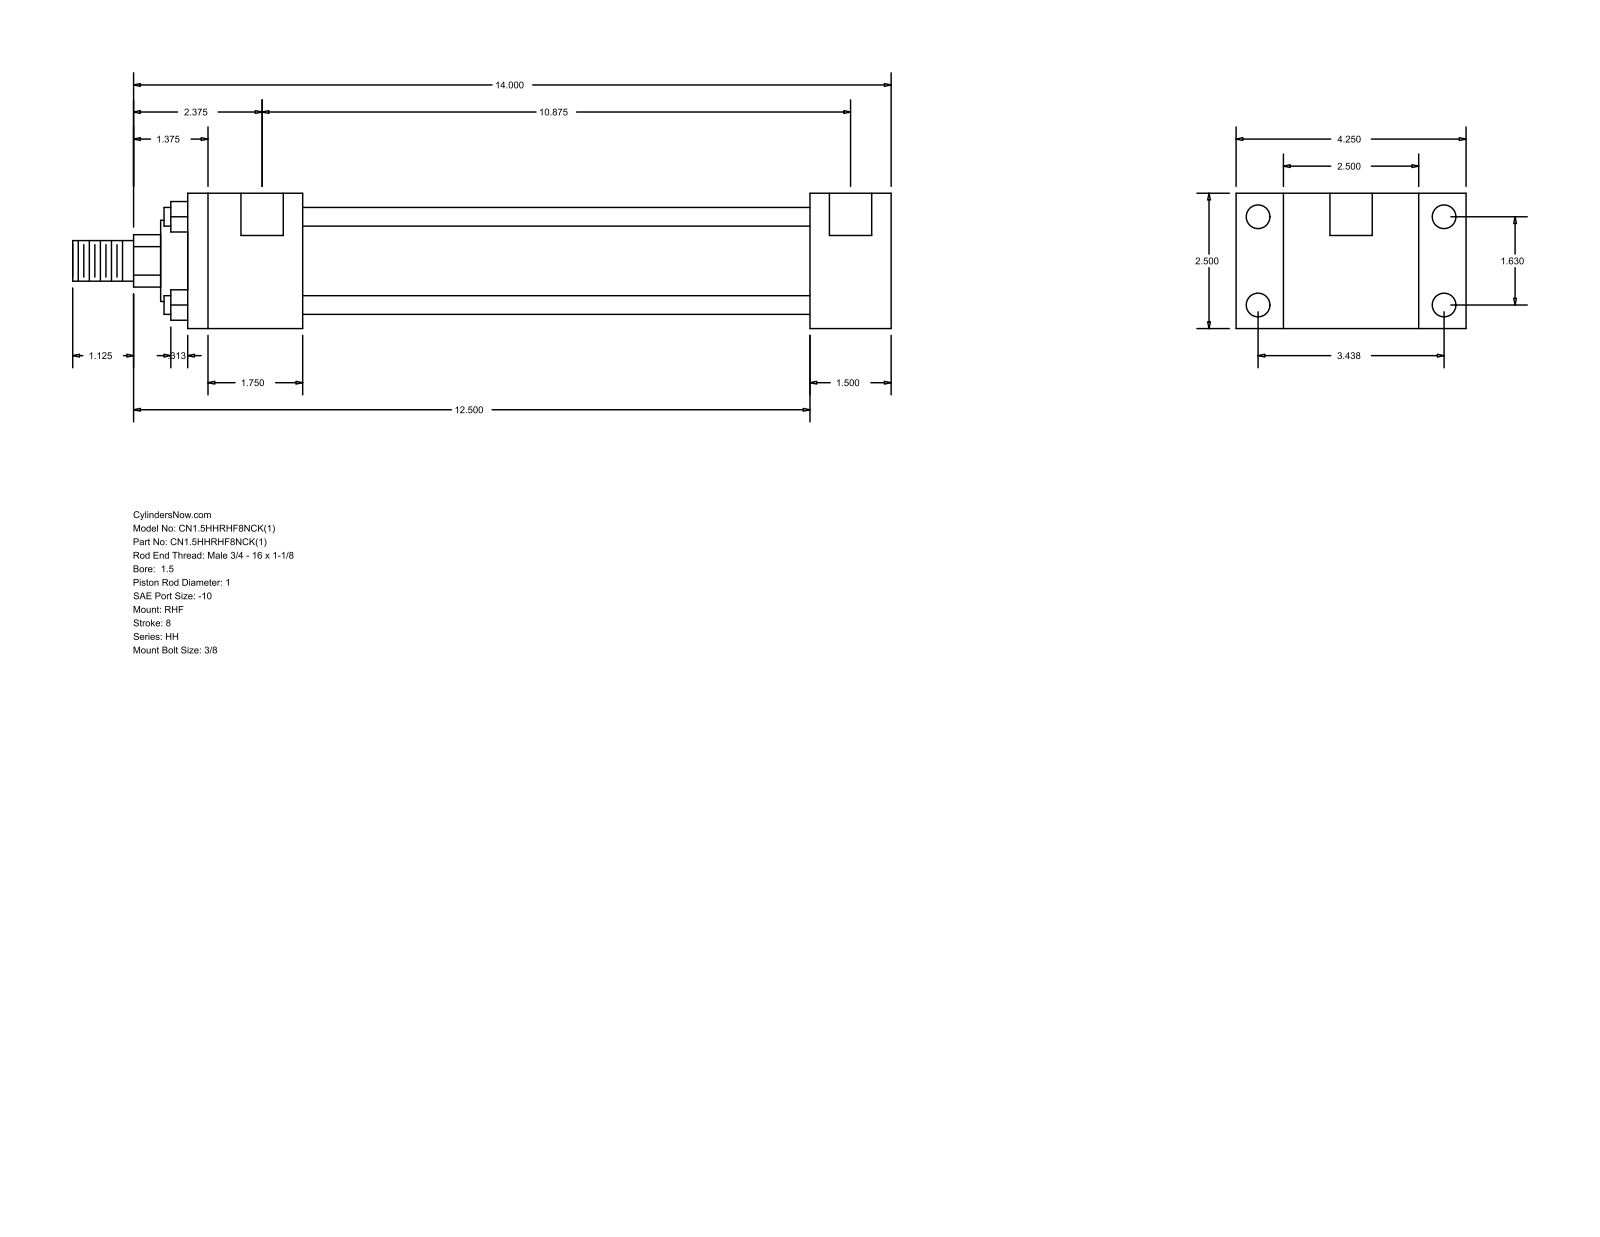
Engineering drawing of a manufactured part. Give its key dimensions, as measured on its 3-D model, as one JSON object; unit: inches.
{"part_name": "HH_RHF__0150_1", "step_written_by": "GSSL Pune (CONFIG_CONTROL_DESIGN)", "units": "inches", "bodies": {"solids": 0, "faces": 88, "planar": 60, "cylindrical": 28, "other": 0}, "overall_size": [15.125, 4.25, 2.5], "round_holes": [[0.219, 4], [0.438, 4], [0.781, 2]], "round_bosses_or_shafts": [[0.345, 4], [1.75, 1], [1.5, 1], [1, 1], [0.75, 1]], "partial_cylinders_radius": [[0.484, 1]], "face_to_face_distances": [2.5, 0.875, 3.375, 1.5, 4.25, 9.375, 10.875, 2.125, 11.5, 13], "hole_center_spacings": [0.063, 1.63, 3.438, 3.805, 10.937, 11, 10.875]}
